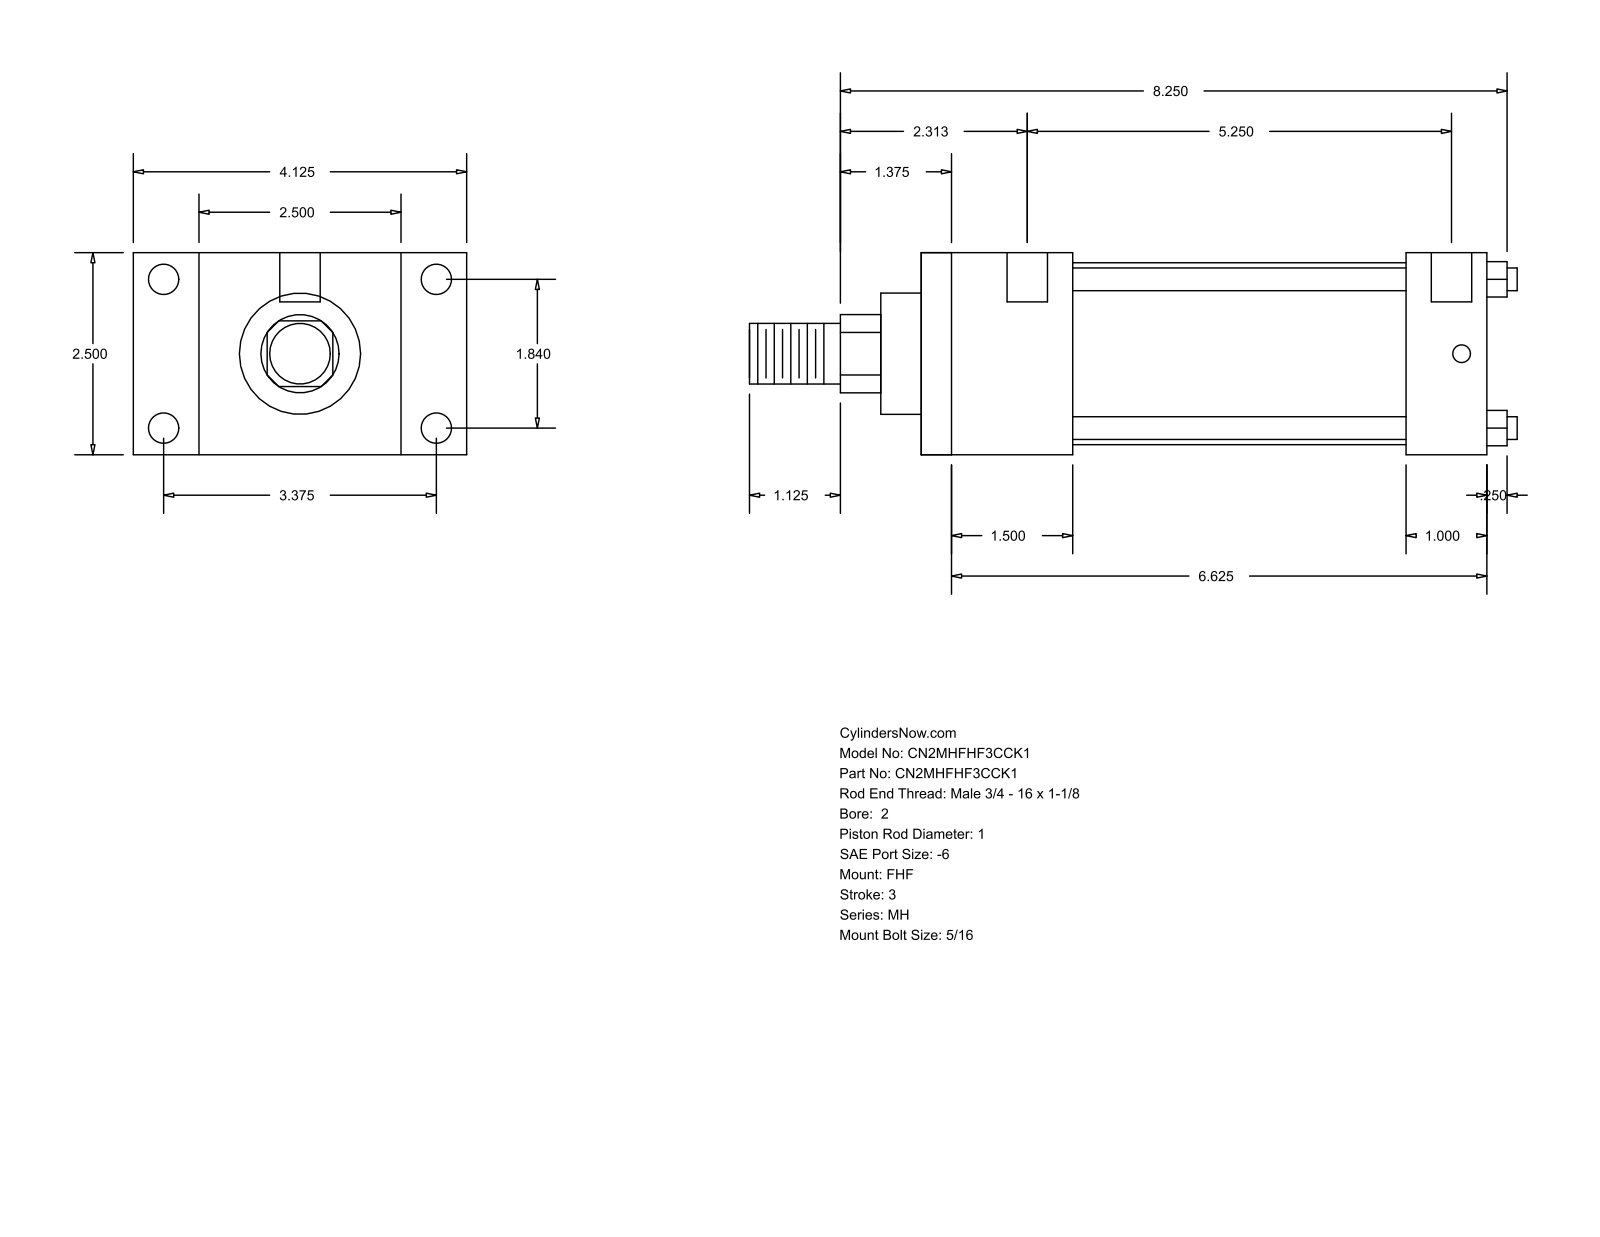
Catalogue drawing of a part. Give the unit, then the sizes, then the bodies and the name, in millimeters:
Units: millimetres
Overall size (bounding box): 241.3 × 104.78 × 63.5
Round holes (diameter × count): ⌀5.56 ×4, ⌀9.53 ×4, ⌀12.7 ×2
Round bosses / shafts (diameter × count): ⌀7.14 ×4, ⌀57.15 ×1, ⌀38.1 ×1, ⌀25.4 ×1, ⌀19.05 ×1
Partial cylindrical surfaces — rounded edges, fillets, slot ends (radius × count): R12.29 ×1
Main face-to-face distances: 63.5, 177.8, 47.63, 130.17, 20.64, 84.14, 104.78, 25.4, 104.77, 152.4
Hole centre spacings: 46.74, 85.72, 97.63, 141.28, 3.17, 4.76, 133.35, 136.52
Bodies: 0 solids, 88 faces (60 planar, 28 cylindrical, 0 other)
Part name (STEP PRODUCT): MH_FHF__0200_1
STEP written by: GSSL Pune (CONFIG_CONTROL_DESIGN)
